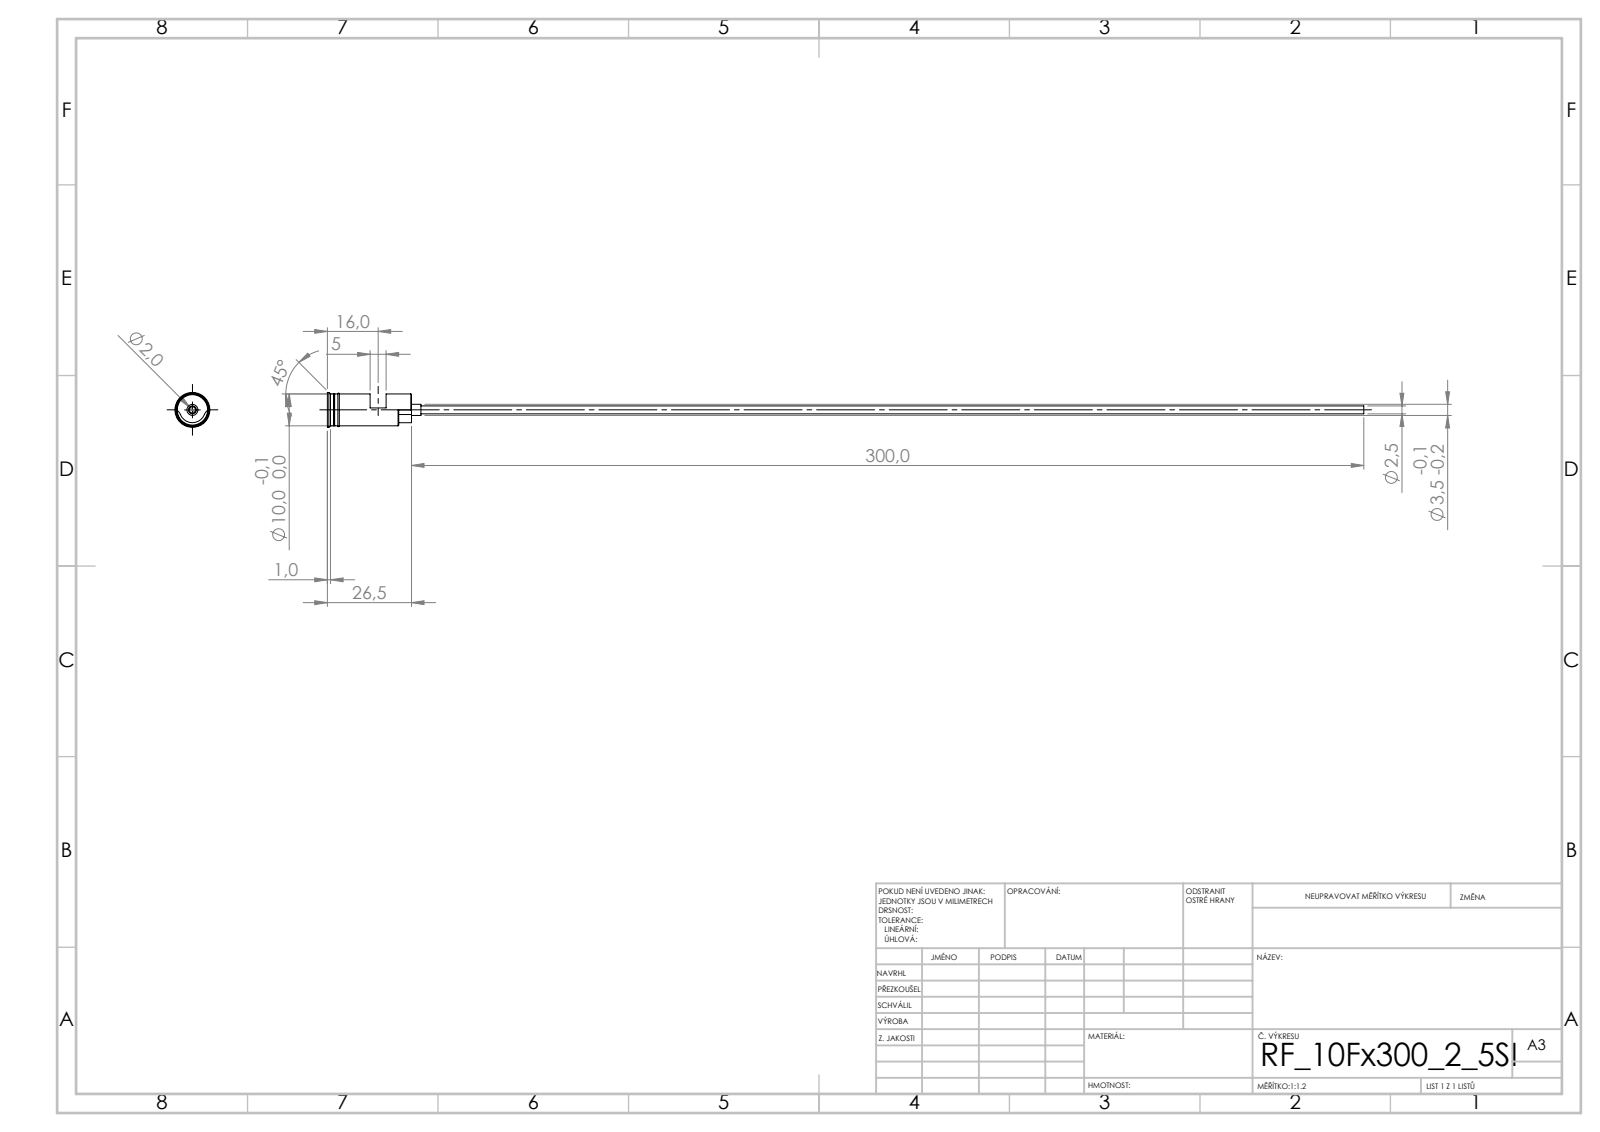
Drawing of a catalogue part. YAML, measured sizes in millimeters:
step_written_by: "SolidWorks 2019 (CONFIG_CONTROL_DESIGN)"
units: millimeters
bodies: {solids: 1, faces: 55, planar: 24, cylindrical: 19, other: 12}
overall_size: [326.5, 11, 11]
volume: 2322
surface_area: 5418
round_holes:
  - {diameter: 2, count: 1}
round_bosses_or_shafts:
  - {diameter: 11, count: 1}
  - {diameter: 10, count: 1}
  - {diameter: 9.8, count: 1}
  - {diameter: 3.5, count: 1}
  - {diameter: 2.5, count: 1}
partial_cylinders:
  - {radius: 3, count: 2}
  - {radius: 4.05, count: 1}
face_to_face_distances: [26.5, 13, 13.5, 8, 5, 18.5, 24.5, 16.5, 11.5, 2]
